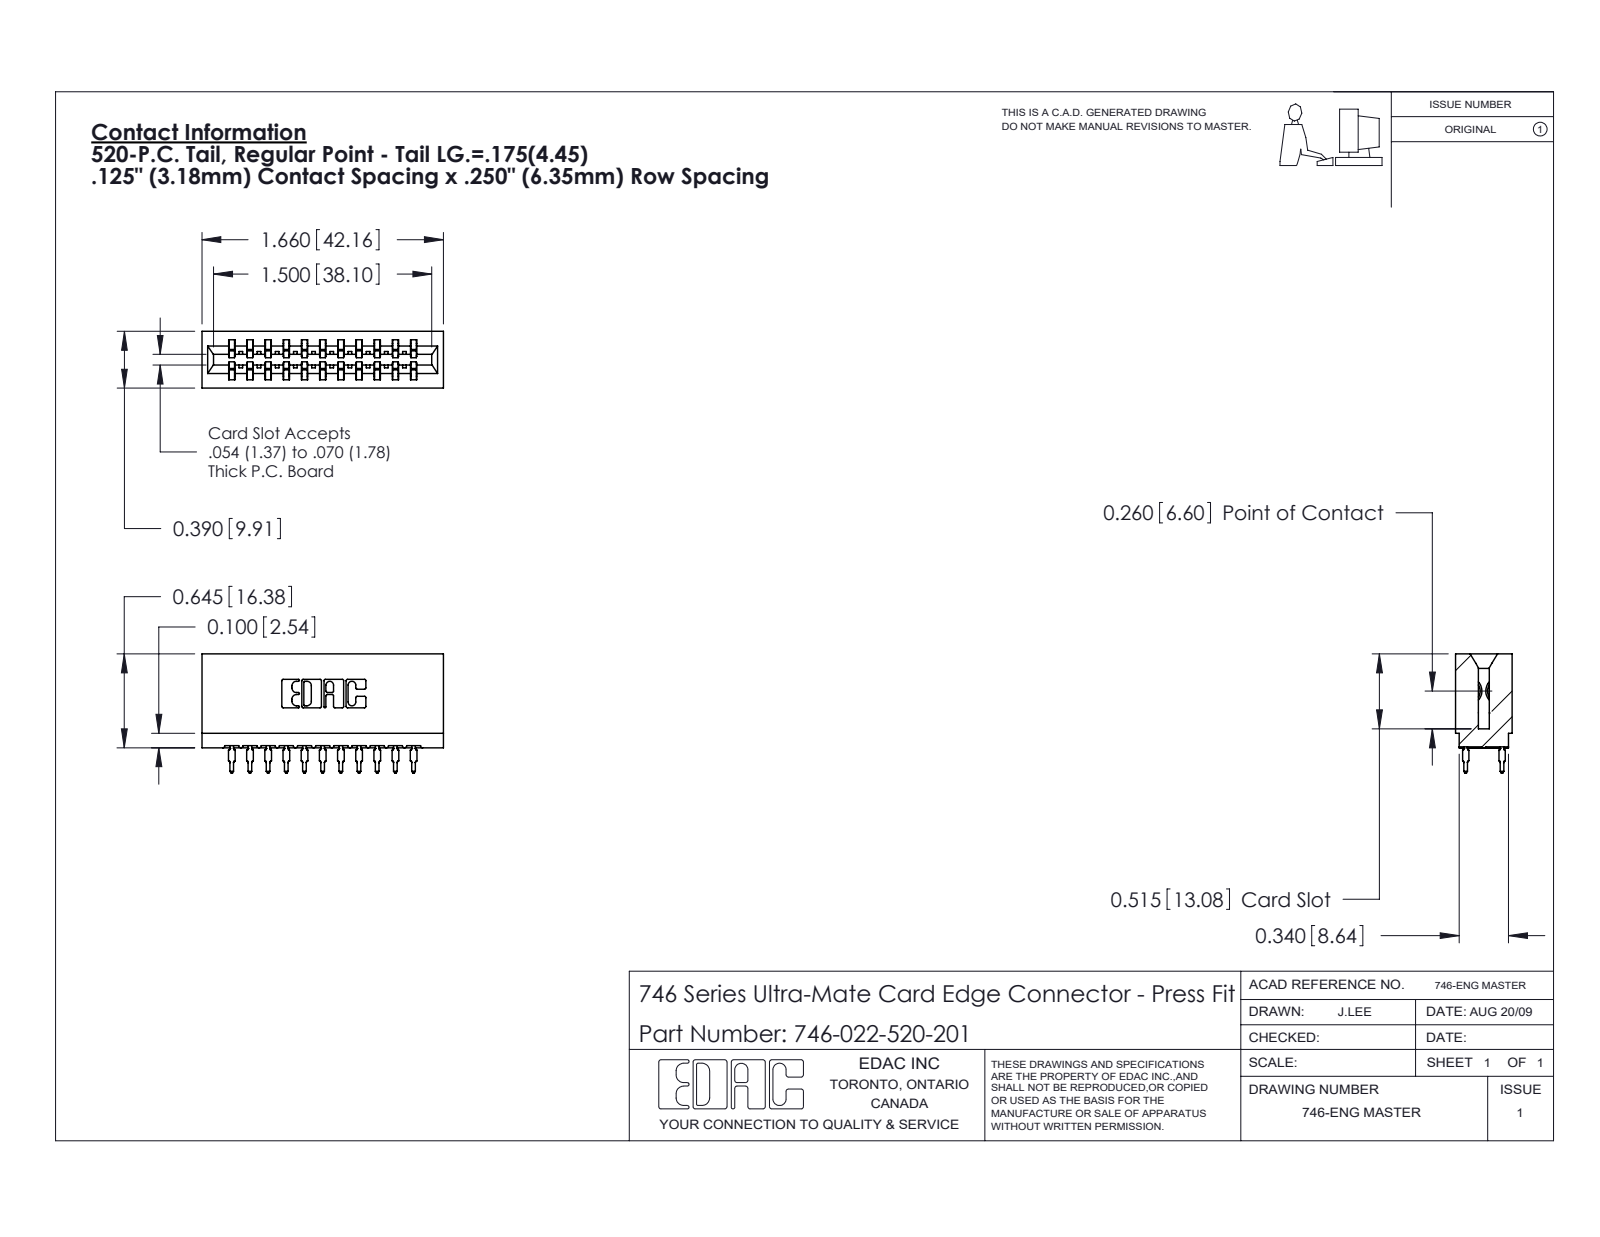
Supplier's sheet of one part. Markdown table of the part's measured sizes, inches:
| quantity | value |
| --- | --- |
| part name | 746 Part_.515 Slot Depth - 01; 746-022-520-201; 746-292-001_520 |
| STEP written by | SolidWorks 2020 (CONFIG_CONTROL_DESIGN) |
| units | inches |
| bodies | 23 solids, 2066 faces (1067 planar, 427 cylindrical, 572 other) |
| overall size | 1.66 × 0.819 × 0.39 |
| volume | 0.287 in³ |
| surface area | 10.58 in² |
| partial cylindrical surfaces (radius × count) | 0.021 × 44, 0.01 × 22, 0.015 × 12, 0.005 × 8, 0.011 × 8, 0.007 × 6, 0.031 × 6, 0.026 × 3 |
| main face-to-face distances | 0.25, 0.333, 0.5, 0.057, 0.125, 0.125, 0.39, 0.042, 0.208, 0.083 |
